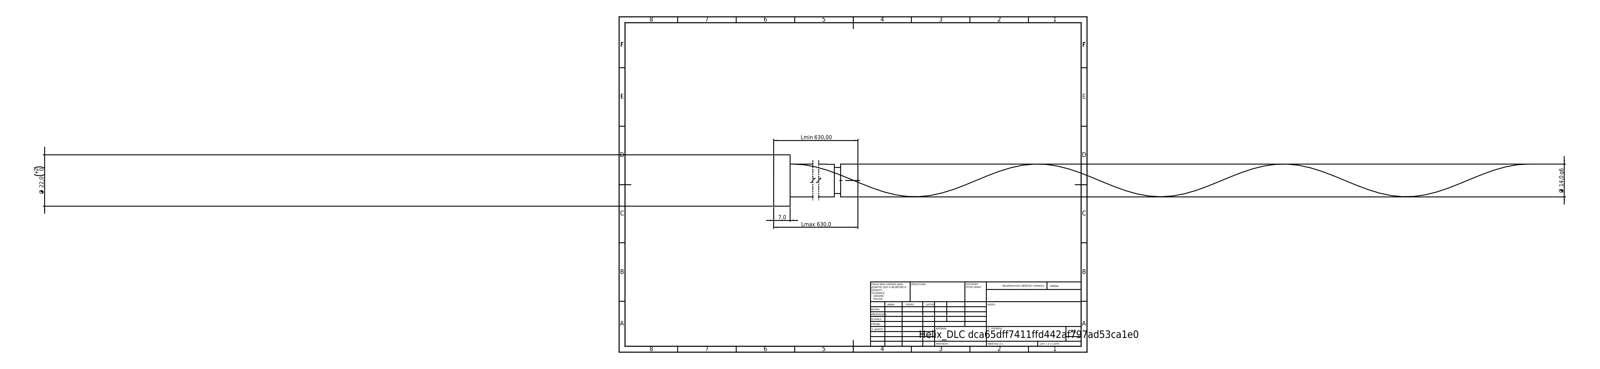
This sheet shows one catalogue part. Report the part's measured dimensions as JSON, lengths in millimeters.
{"step_written_by": "SolidWorks 2019 (CONFIG_CONTROL_DESIGN)", "units": "millimeters", "bodies": {"solids": 1, "faces": 21, "planar": 6, "cylindrical": 14, "other": 1}, "overall_size": [630, 22, 22], "volume_mm3": 97481, "surface_area_mm2": 29196, "round_bosses_or_shafts": [[22, 1], [14, 1], [11.2, 1]], "face_to_face_distances": [7, 630, 623, 622.65, 615.65, 7.35, 619.85, 612.85, 2.8, 10.15]}
